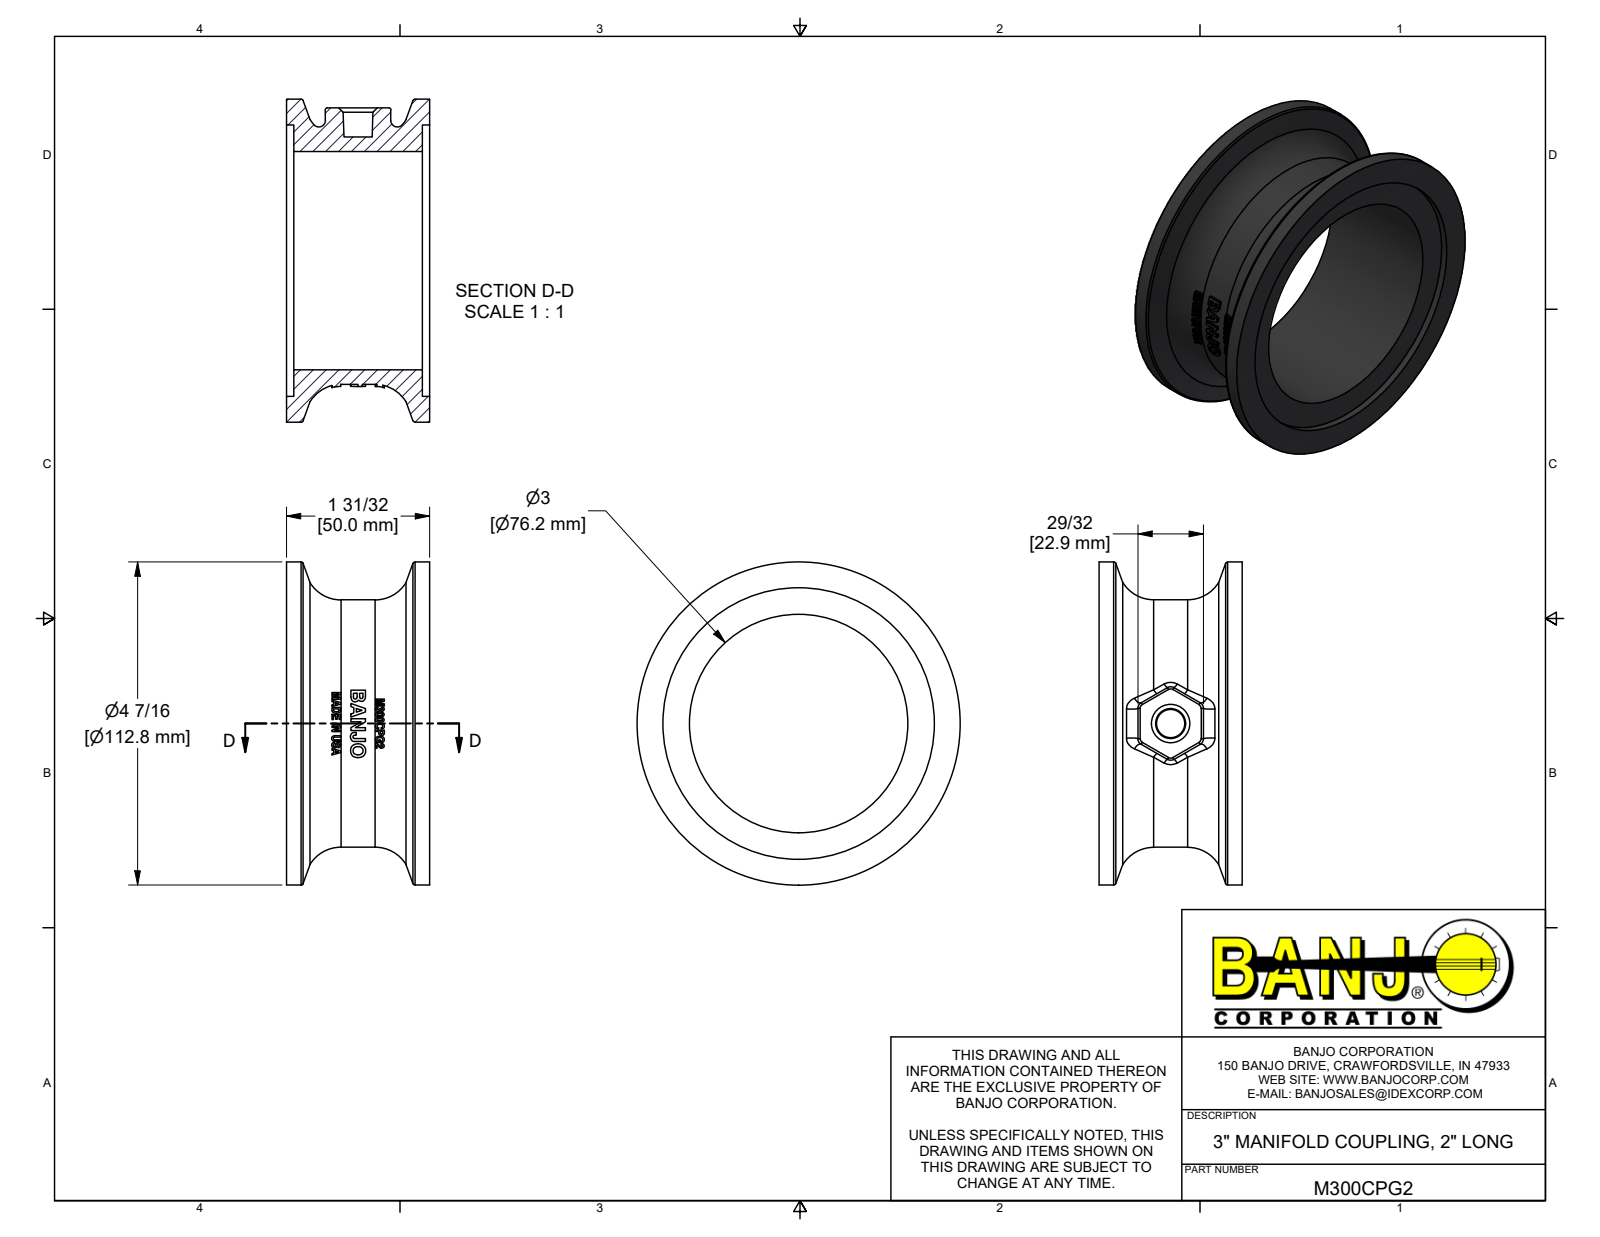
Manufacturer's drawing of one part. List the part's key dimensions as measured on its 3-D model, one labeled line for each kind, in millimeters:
Part name (STEP PRODUCT): M300CPG2
STEP written by: Autodesk Inventor 2022 (AUTOMOTIVE_DESIGN)
Units: millimetres
Bodies: 1 solid, 377 faces (163 planar, 27 cylindrical, 187 other)
Overall size (bounding box): 112.8 × 112.8 × 50
Volume: 128 900 mm³ · Surface area: 43 890 mm²
Round holes (diameter × count): ⌀76.2 ×1, ⌀94.7 ×1
Round bosses / shafts (diameter × count): ⌀112.8 ×1, ⌀86.4 ×1
Partial cylindrical surfaces — rounded edges, fillets, slot ends (radius × count): R0.8 ×6, R2.3 ×6, R43.9 ×1
Main face-to-face distances: 2.5, 47.5, 50, 44.9, 22.9, 13.6, 36.4, 11, 33.9, 10.2
